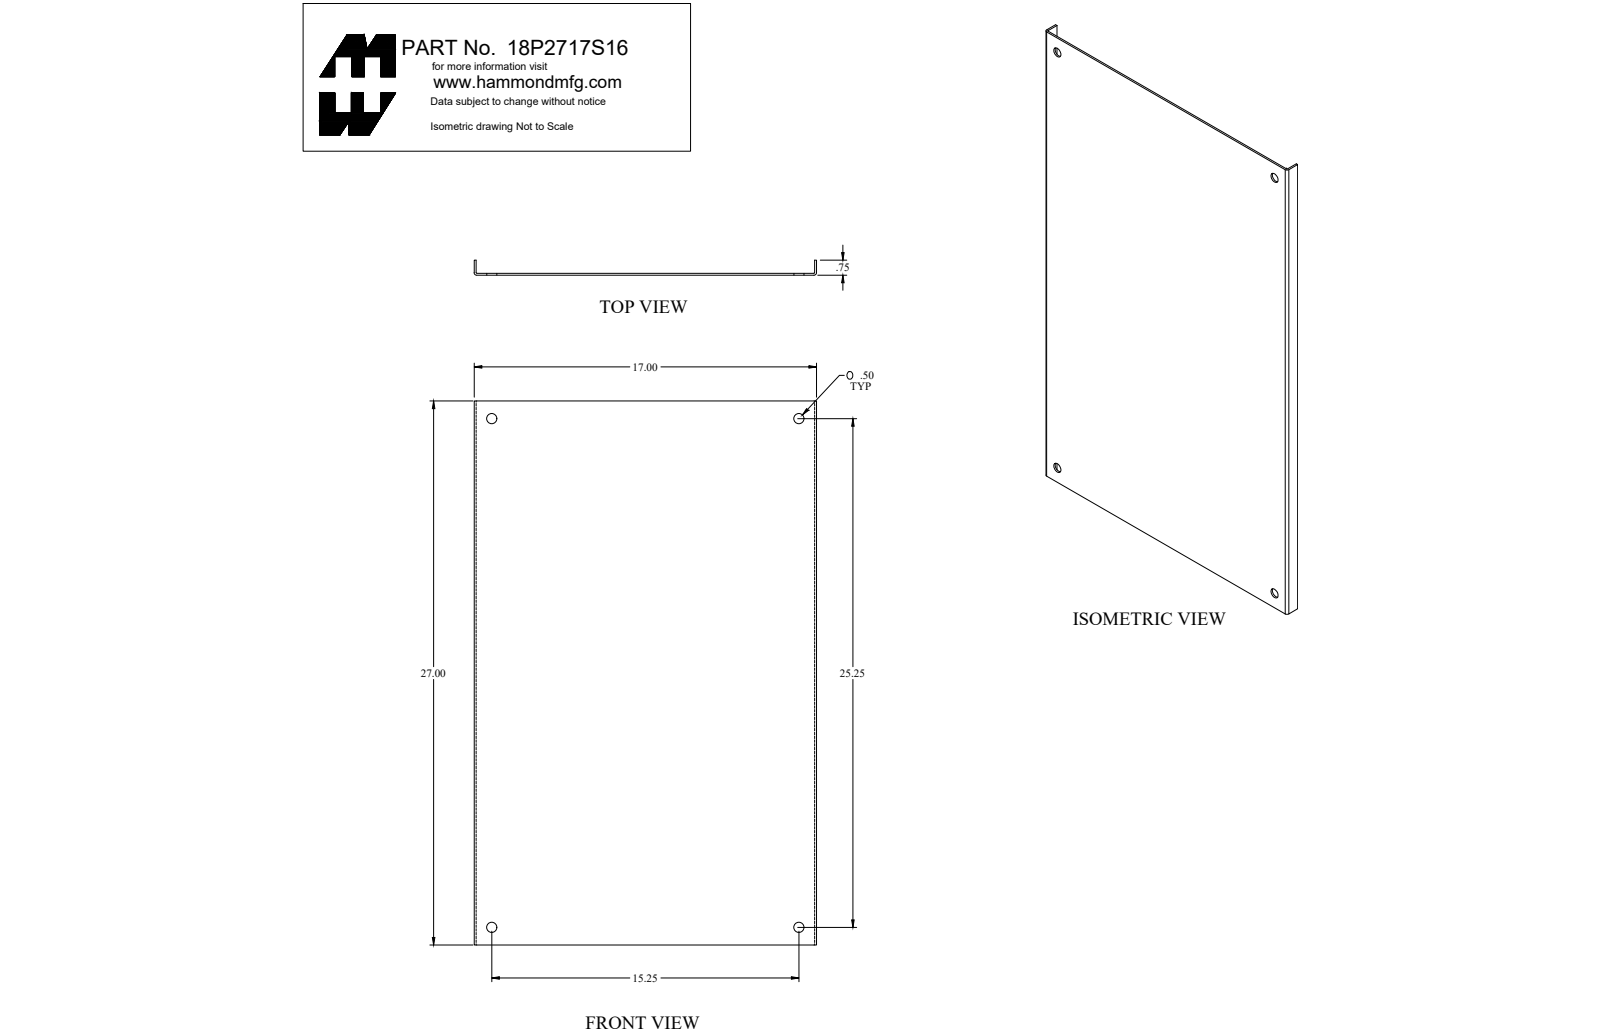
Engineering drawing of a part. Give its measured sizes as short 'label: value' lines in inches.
name: 18P2717S16_Default
written by: SolidWorks 2018 (CONFIG_CONTROL_DESIGN)
unit: in
bodies: 1 solid, 22 faces (10 planar, 12 cylindrical, 0 other)
size: 27 × 17 × 0.75
volume: 46.72 in³; area: 992.8 in²
holes: 4× ⌀0.5
rounds: 2× R0.03, 2× R0.125
face distances: 0.095, 16.905, 17, 16.81, 0.75, 0.655, 27
hole spacings: 15.25, 25.25, 29.498
